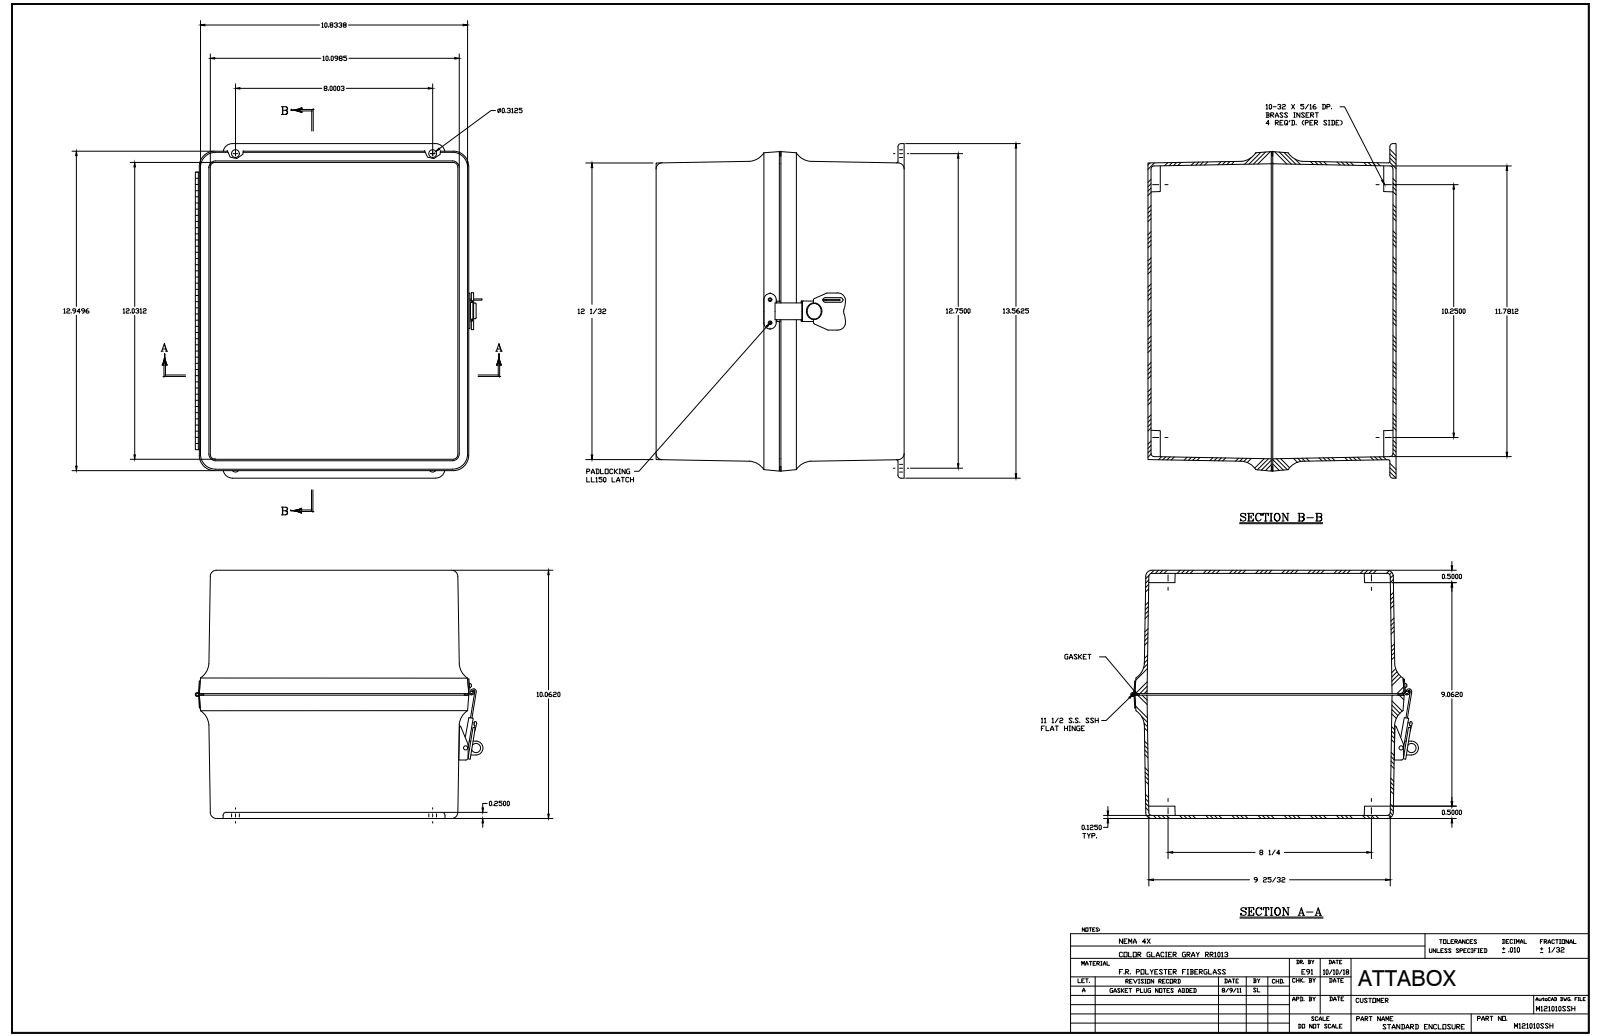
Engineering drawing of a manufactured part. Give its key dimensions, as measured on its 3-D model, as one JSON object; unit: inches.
{"part_name": "M121010SSH", "step_written_by": "SolidWorks 2018 (AUTOMOTIVE_DESIGN)", "units": "inches", "bodies": {"solids": 37, "faces": 1227, "planar": 453, "cylindrical": 472, "other": 302}, "overall_size": [13.563, 11.62, 10.049], "volume_in3": 114.8, "surface_area_in2": 1499, "round_holes": [[0.14, 12], [0.152, 11], [0.136, 8], [0.156, 6], [0.218, 4], [0.13, 2], [0.165, 2], [0.197, 2], [0.085, 1], [0.106, 1], [0.118, 1], [0.138, 1]], "round_bosses_or_shafts": [[0.25, 12], [0.125, 8], [0.27, 6], [0.125, 4], [0.583, 1], [0.524, 1], [0.209, 1], [0.185, 1]], "partial_cylinders_radius": [[0.031, 88], [0.75, 13], [0.125, 12], [0.25, 12], [0.079, 10], [0.037, 4], [0.039, 4], [0.045, 4]], "face_to_face_distances": [0.125, 9.798, 10.048, 9.938, 0.125, 9.924, 9.923, 11.96, 10.196, 12.218], "hole_center_spacings": [3.625, 6.875, 9.252, 11.243, 0.672, 1.348, 10.5, 14.498]}
